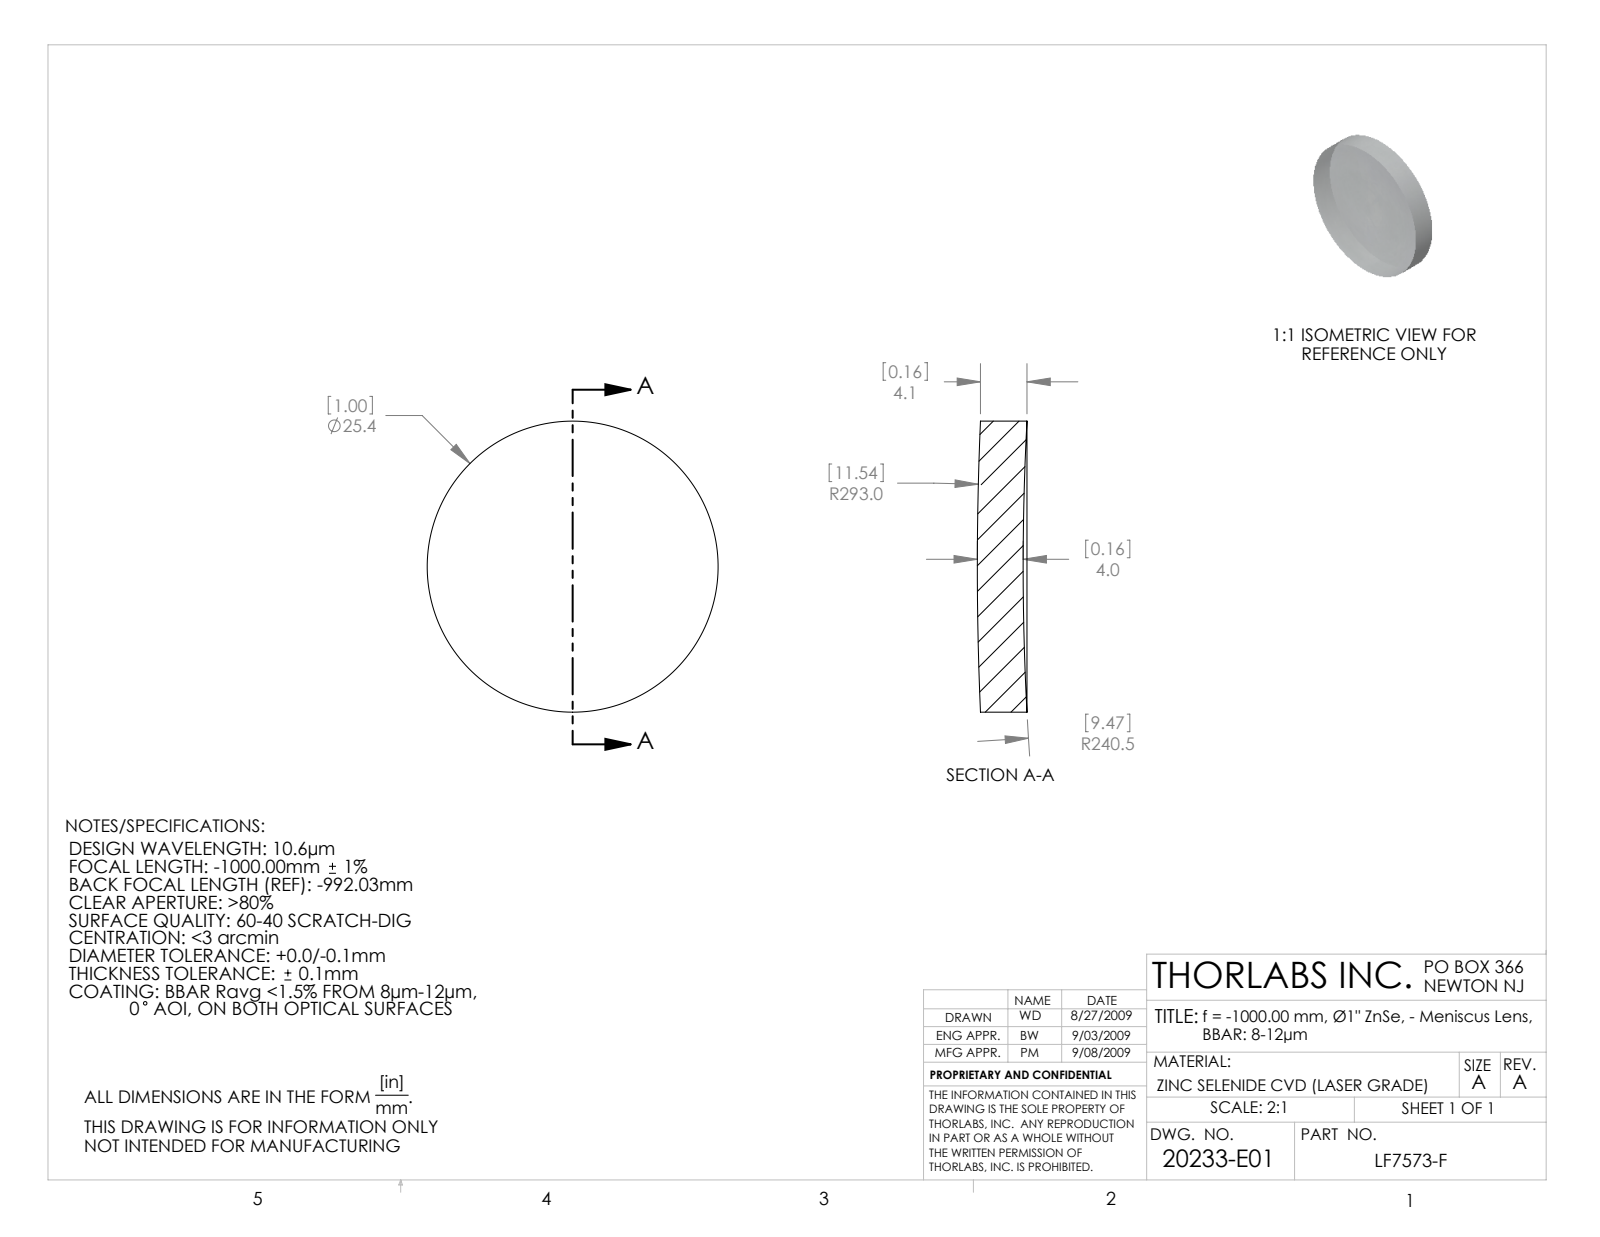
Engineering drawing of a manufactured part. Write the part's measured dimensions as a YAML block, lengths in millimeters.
part_name: "20233-E0W"
step_written_by: "SolidWorks 2007 (CONFIG_CONTROL_DESIGN)"
units: millimeters
bodies: {solids: 1, faces: 6, planar: 0, cylindrical: 2, other: 4}
overall_size: [25.4, 25.4, 4.34]
volume: 2042
surface_area: 1338
round_bosses_or_shafts:
  - {diameter: 25.4, count: 1}
